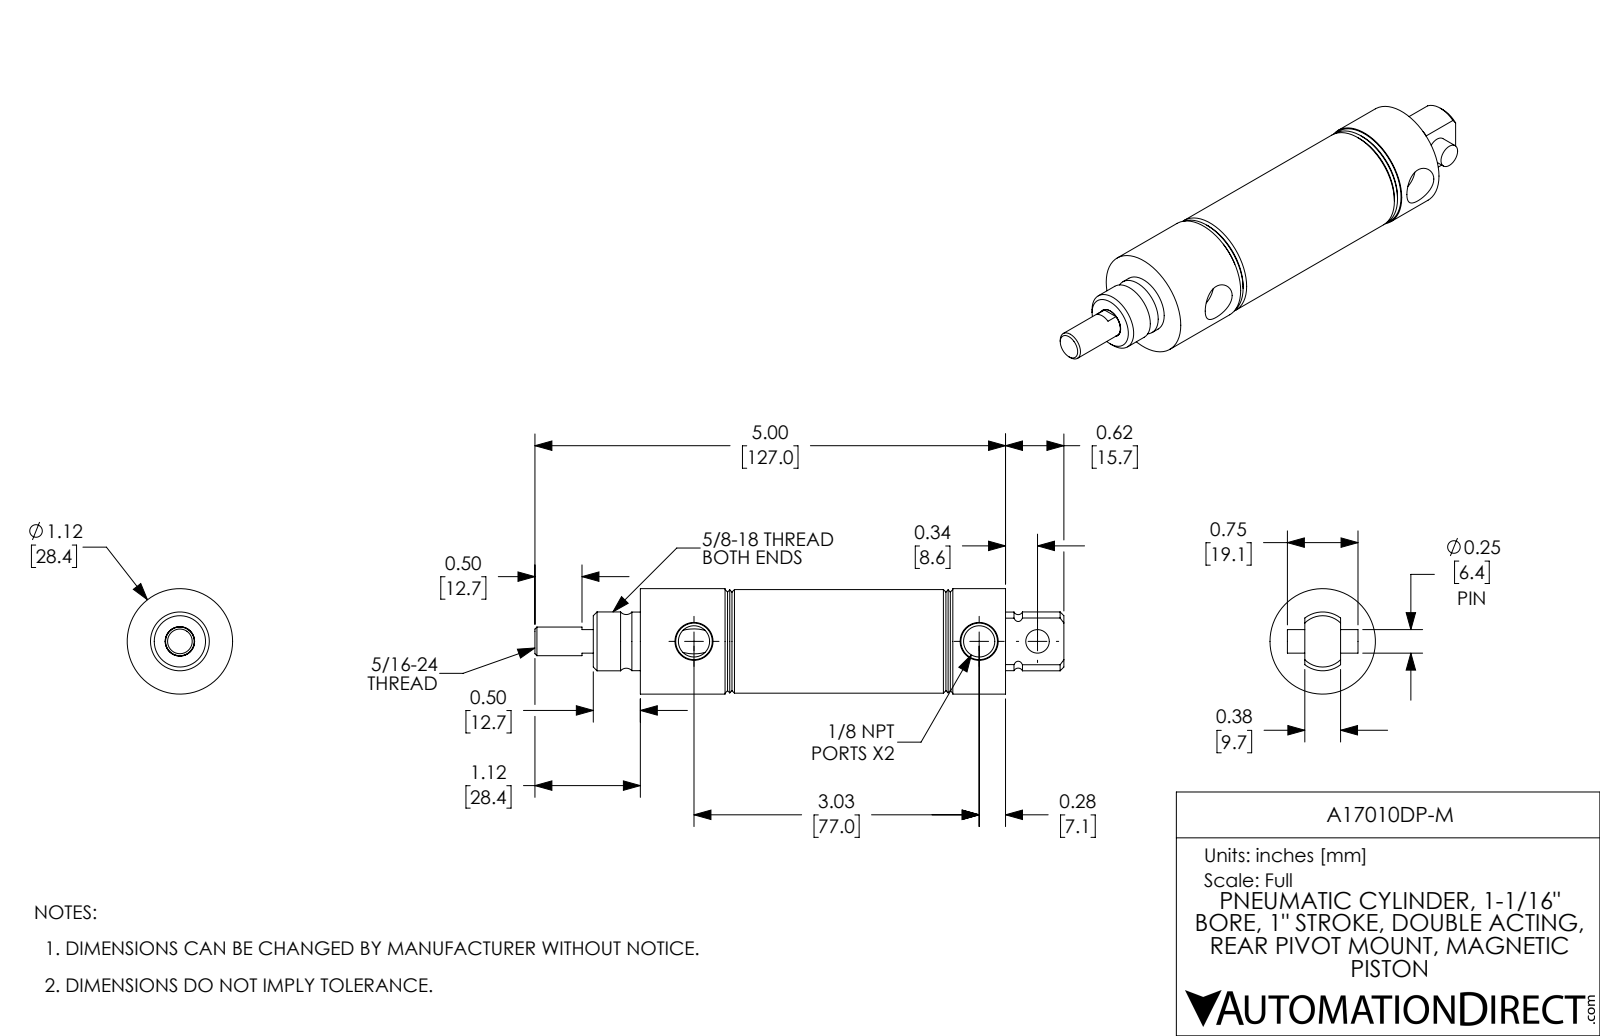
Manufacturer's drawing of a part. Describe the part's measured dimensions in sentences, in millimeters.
The part is named "A17010DP-M; A17010DP-M-PIN; A17010DP-M-Rod; A17010DP-M-MainBody". Its 3-D file was written by "SolidWorks 2017 (AUTOMOTIVE_DESIGN)". It is 3 solids with 92 faces: 22 planar, 32 cylindrical and 38 other. Overall it measures 142.7 by 28.4 by 28.4 millimeters. Its volume is 51 880 cubic millimeters and its surface area 22 280 square millimeters. Round holes: 2 of diameter 8.4, 1 of diameter 6.4, 1 of diameter 7.9, 1 of diameter 27. Round bosses or shafts: 1 of diameter 28.4, 1 of diameter 27.9, 1 of diameter 15.9, 1 of diameter 15.8, 1 of diameter 7.7. Partial cylindrical surfaces (rounded edges, fillets, slot ends): 1 of radius 8. The main face-to-face distances are 12.7, 68.3, 38.1, 25.4, 30.2, 42.9, 68.3, 98.6, 55.6, 30.2. The hole center spacings are 15.7, 77, 92.7.
